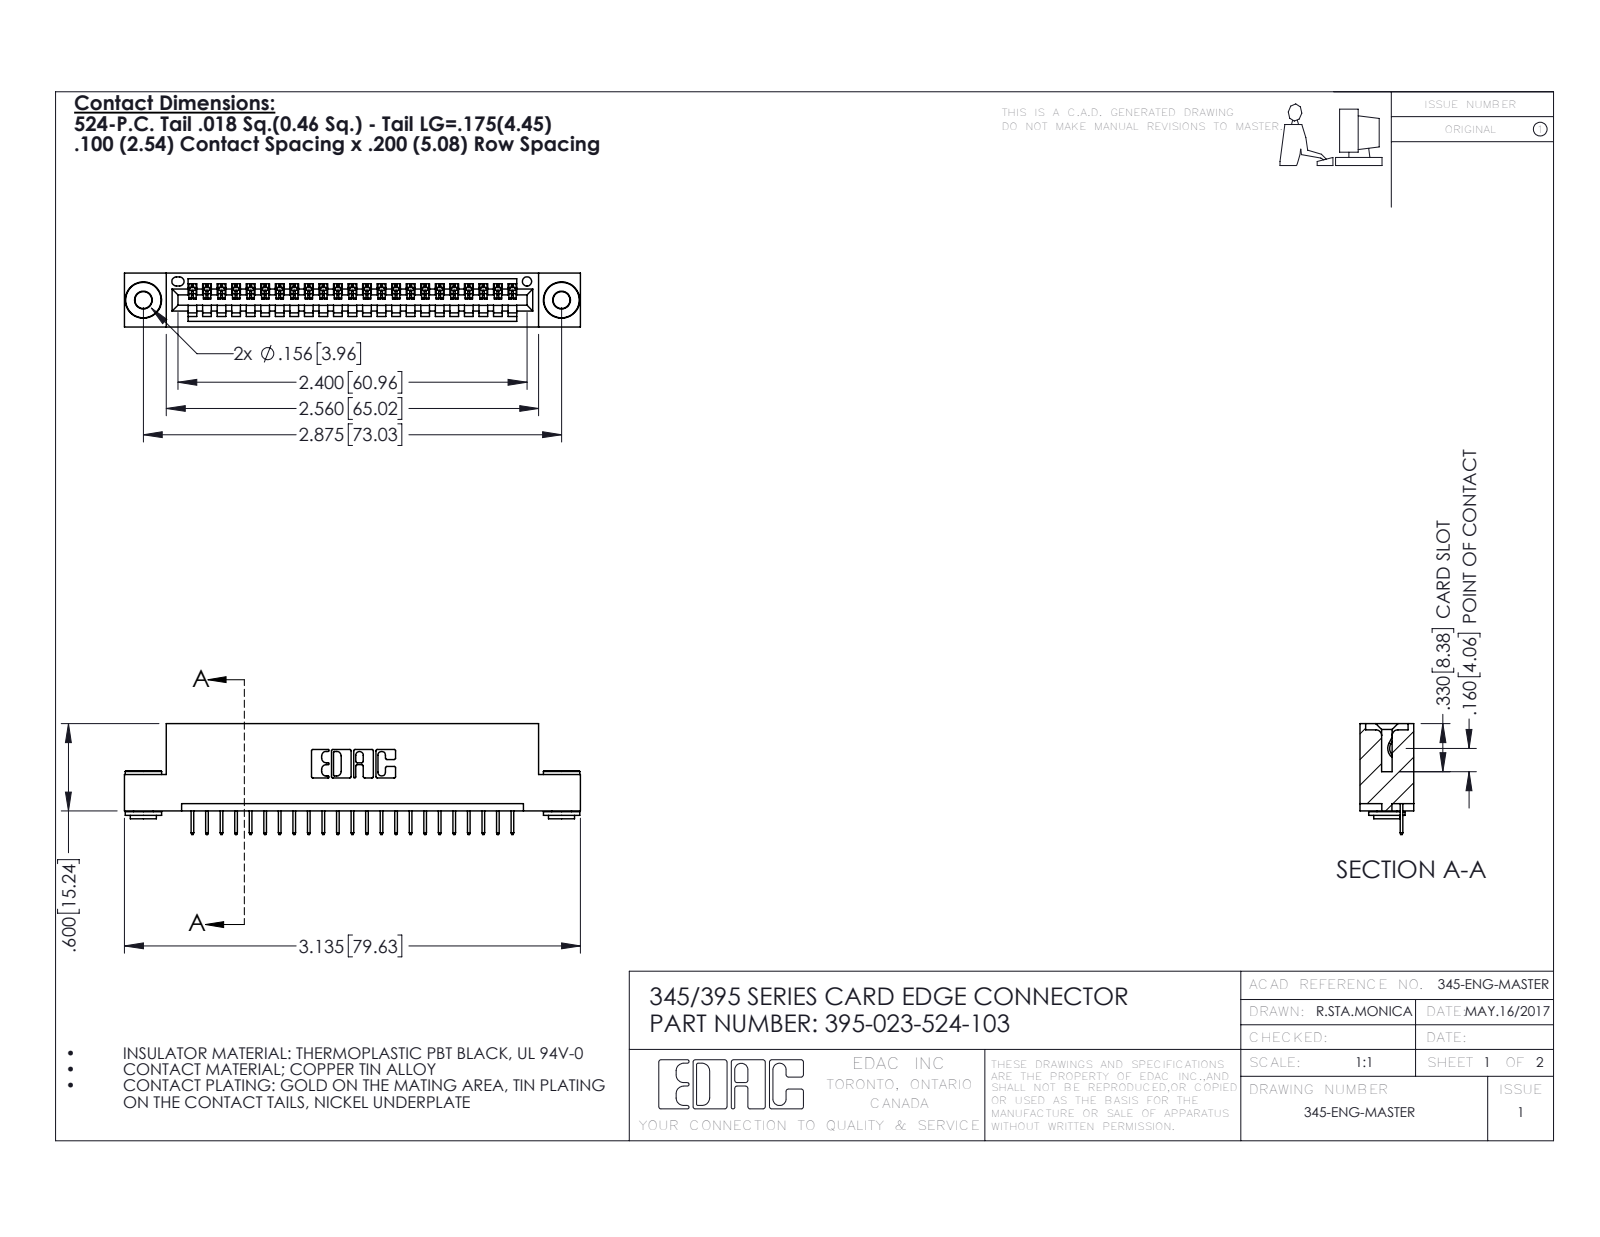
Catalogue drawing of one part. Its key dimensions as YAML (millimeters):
part_name: "345-292-001_345-293-124; 395-023-524-103; 345 Part_Flush Mounting Lugs - 0.156 Dia-TH; 345-250-002_345-250-002-102"
step_written_by: "SolidWorks 2016 (CONFIG_CONTROL_DESIGN)"
units: millimeters
bodies: {solids: 26, faces: 1590, planar: 1148, cylindrical: 434, other: 8}
overall_size: [79.6, 19.4, 9.4]
volume: 7340
surface_area: 9413
round_holes:
  - {diameter: 2.9, count: 2}
  - {diameter: 4, count: 2}
  - {diameter: 1.6, count: 1}
round_bosses_or_shafts:
  - {diameter: 6.4, count: 2}
  - {diameter: 4.6, count: 2}
  - {diameter: 3.5, count: 2}
partial_cylinders:
  - {radius: 0.2, count: 46}
  - {radius: 0.3, count: 22}
  - {radius: 0.2, count: 6}
  - {radius: 0.8, count: 6}
  - {radius: 0.7, count: 3}
  - {radius: 0.8, count: 2}
  - {radius: 1, count: 2}
  - {radius: 0.4, count: 1}
face_to_face_distances: [1.8, 7.6, 5.1, 9.4, 0.6, 2.5, 6.9, 5.7, 1.8, 3.8]
hole_center_spacings: [6.9, 67.1, 73]
